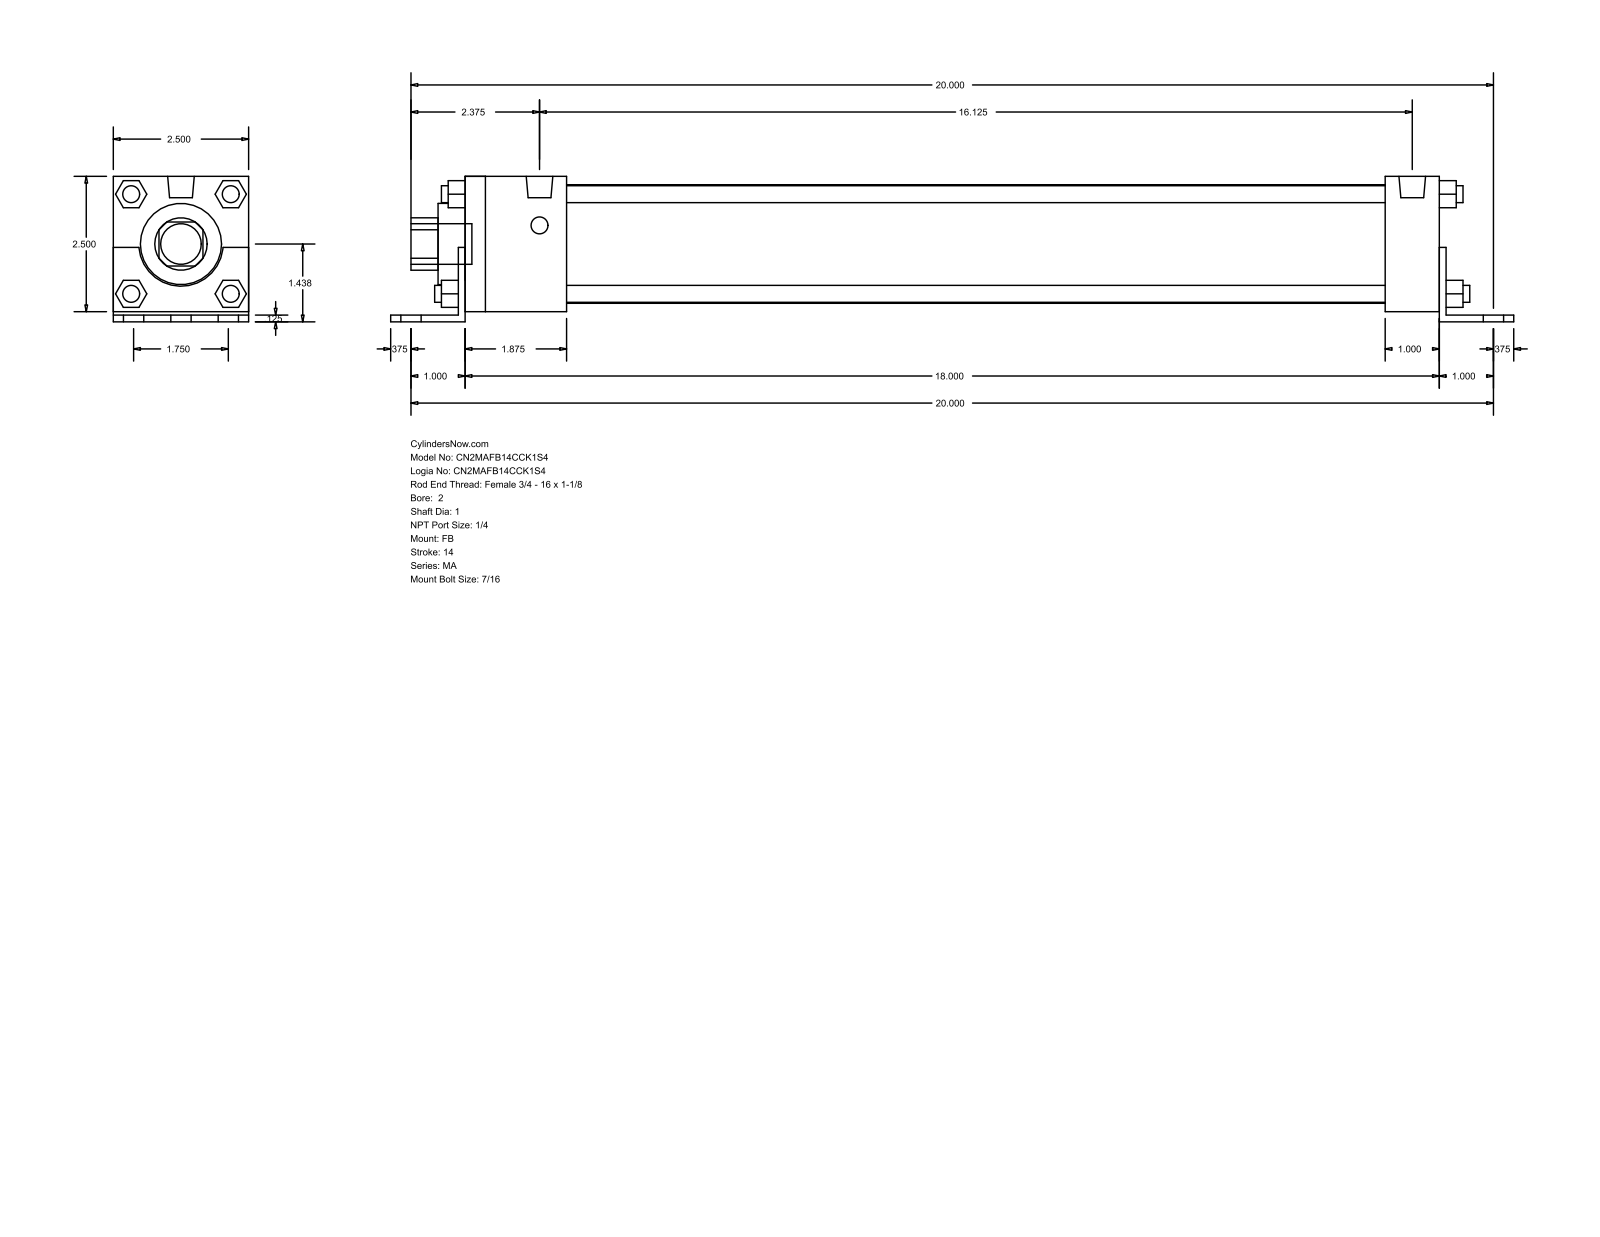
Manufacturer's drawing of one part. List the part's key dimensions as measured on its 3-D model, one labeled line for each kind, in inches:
Part name (STEP PRODUCT): MA_FB__0200_1
STEP written by: GSSL Pune (CONFIG_CONTROL_DESIGN)
Units: inches
Bodies: 0 solids, 140 faces (105 planar, 35 cylindrical, 0 other)
Overall size (bounding box): 20.75 × 2.687 × 2.5
Round holes (diameter × count): ⌀1 ×1, ⌀1.5 ×1, ⌀2.19 ×1
Round bosses / shafts (diameter × count): ⌀0.313 ×8, ⌀0.437 ×6, ⌀0.492 ×2, ⌀0.75 ×1
Partial cylindrical surfaces — rounded edges, fillets, slot ends (radius × count): R0.484 ×1, R0.78 ×1
Main face-to-face distances: 2.5, 0.125, 0.187, 2.687, 0.063, 2.563, 18.125, 0.5, 18, 1
